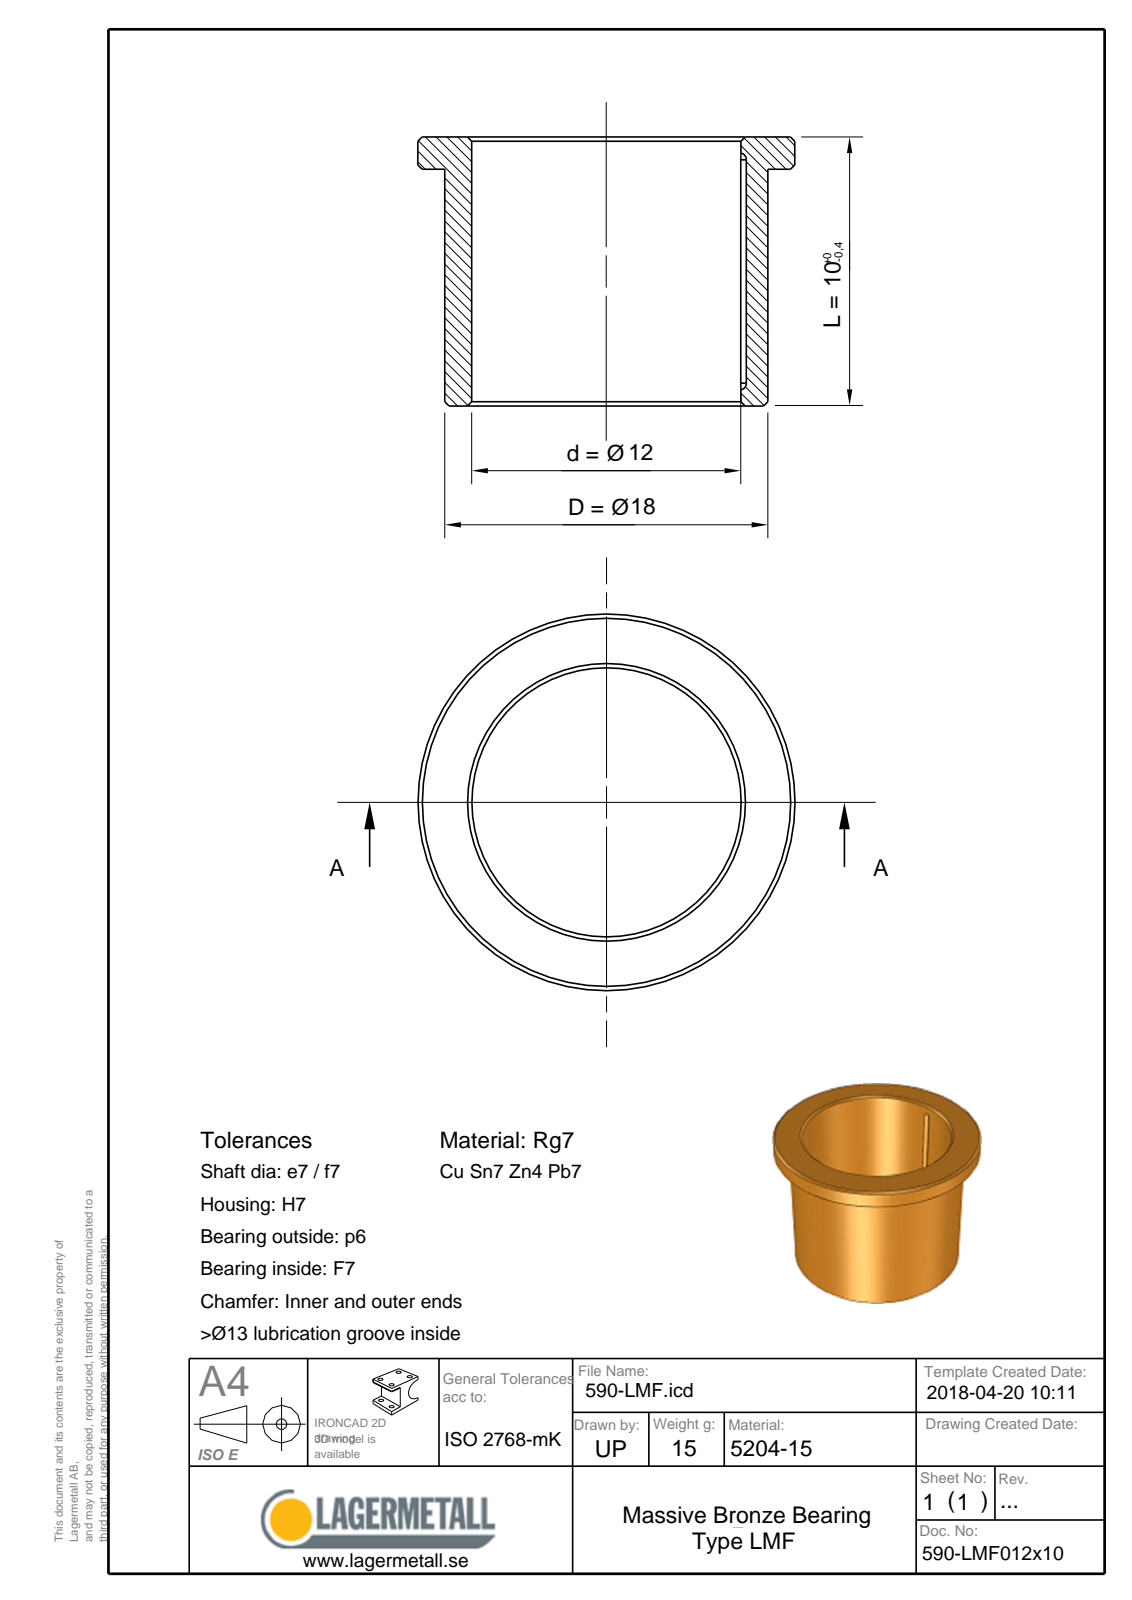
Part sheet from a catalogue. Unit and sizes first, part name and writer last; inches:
Units: inches
Overall size (bounding box): 0.866 × 0.866 × 0.394
Round holes (diameter × count): ⌀0.472 ×1
Round bosses / shafts (diameter × count): ⌀0.866 ×1, ⌀0.709 ×1
Main face-to-face distances: 0.394, 0.276, 0.118
Volume: 0.107 in³ · Surface area: 2.224 in²
Bodies: 1 solid, 11 faces (3 planar, 3 cylindrical, 5 other)
Part name (STEP PRODUCT): 590-LMF012x10
STEP written by: Spatial InterOp 3D (CONFIG_CONTROL_DESIGN)
